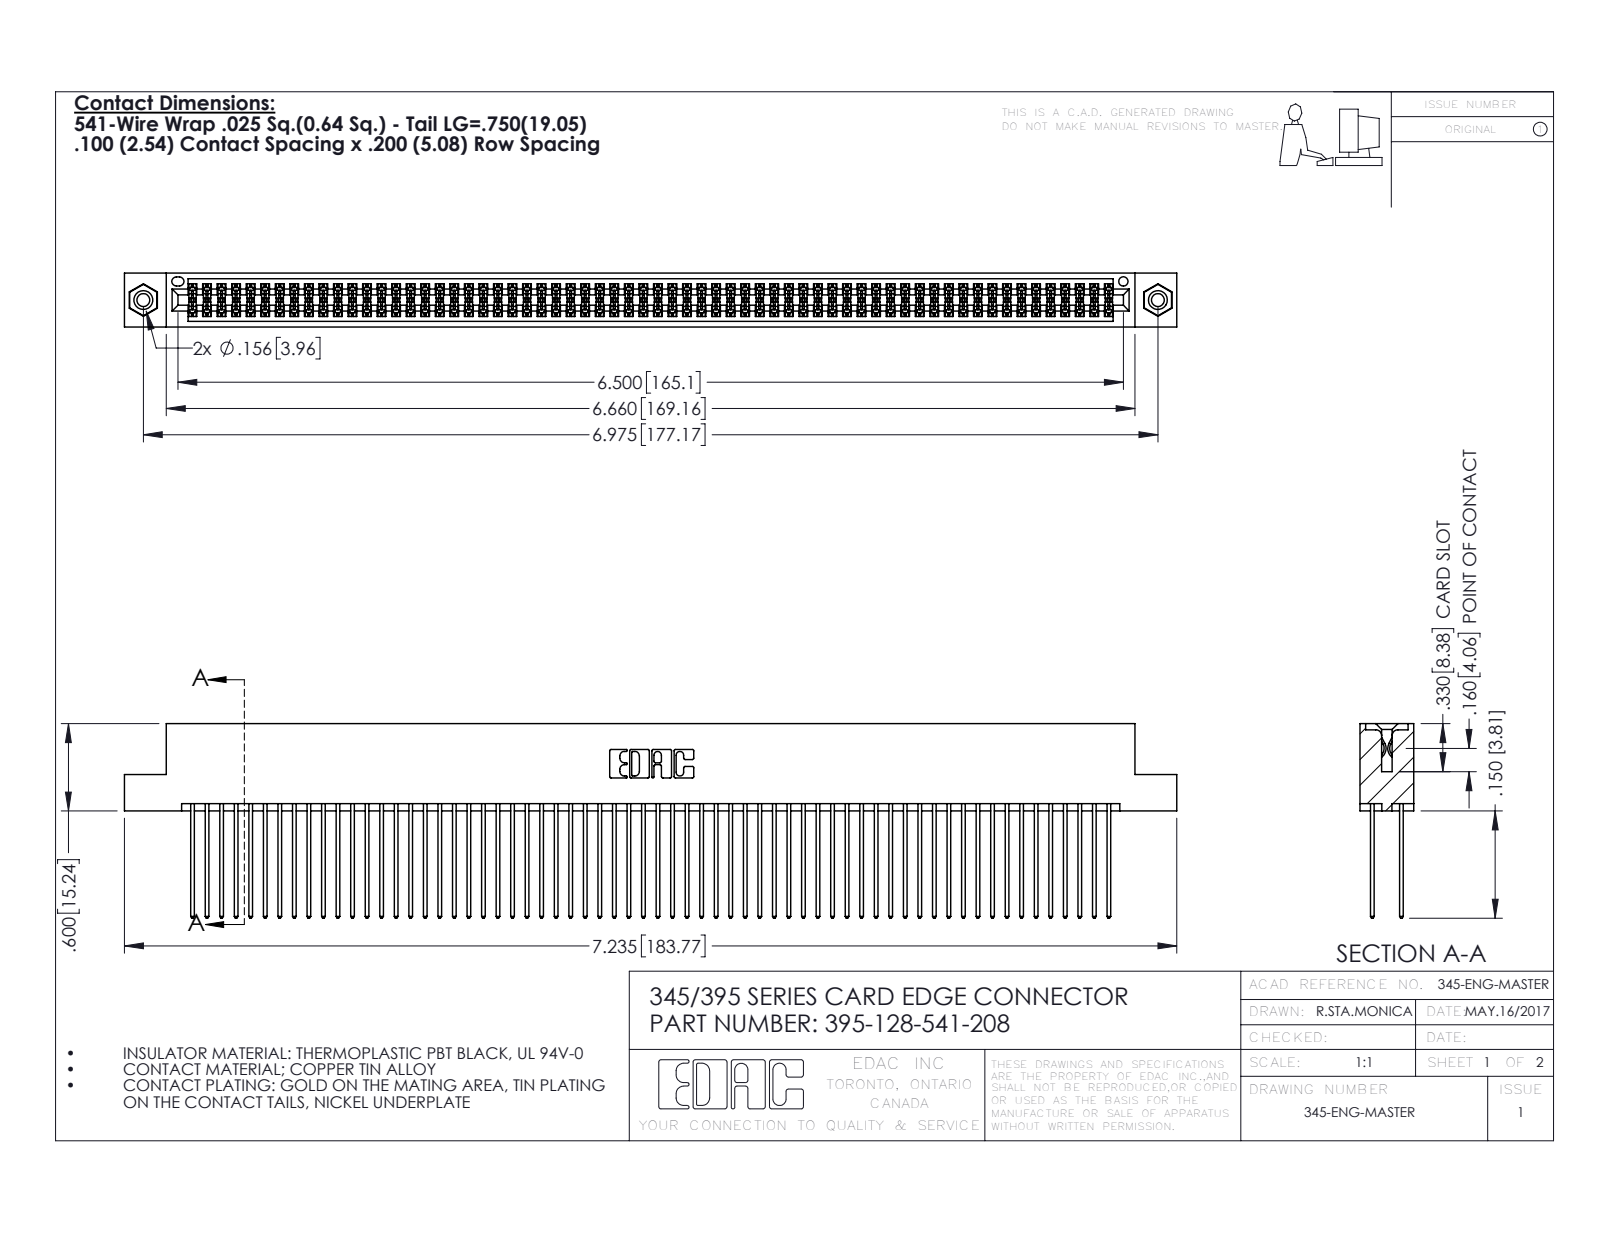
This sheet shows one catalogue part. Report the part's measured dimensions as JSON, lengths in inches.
{"part_name": "395-128-541-208; 345 Part_Flush Mounting Lugs - 0.156 Dia-TI; 345-250-001_345-250-003-102; 345-292-001_345-293-141", "step_written_by": "SolidWorks 2016 (CONFIG_CONTROL_DESIGN)", "units": "inches", "bodies": {"solids": 131, "faces": 6586, "planar": 4336, "cylindrical": 2234, "other": 16}, "overall_size": [7.235, 1.337, 0.37], "volume_in3": 1.146, "surface_area_in2": 49.07, "round_holes": [[0.089, 2], [0.125, 2], [0.156, 2], [0.064, 1]], "round_bosses_or_shafts": [[0.155, 2]], "partial_cylinders_radius": [[0.006, 192], [0.01, 128], [0.01, 22], [0.007, 6], [0.031, 6], [0.026, 3], [0.014, 2], [0.019, 2]], "face_to_face_distances": [0.072, 0.298, 0.2, 0.098, 0.272, 0.025, 0.225, 0.37, 0.175, 0.149], "hole_center_spacings": [0.27, 6.739, 6.975]}
